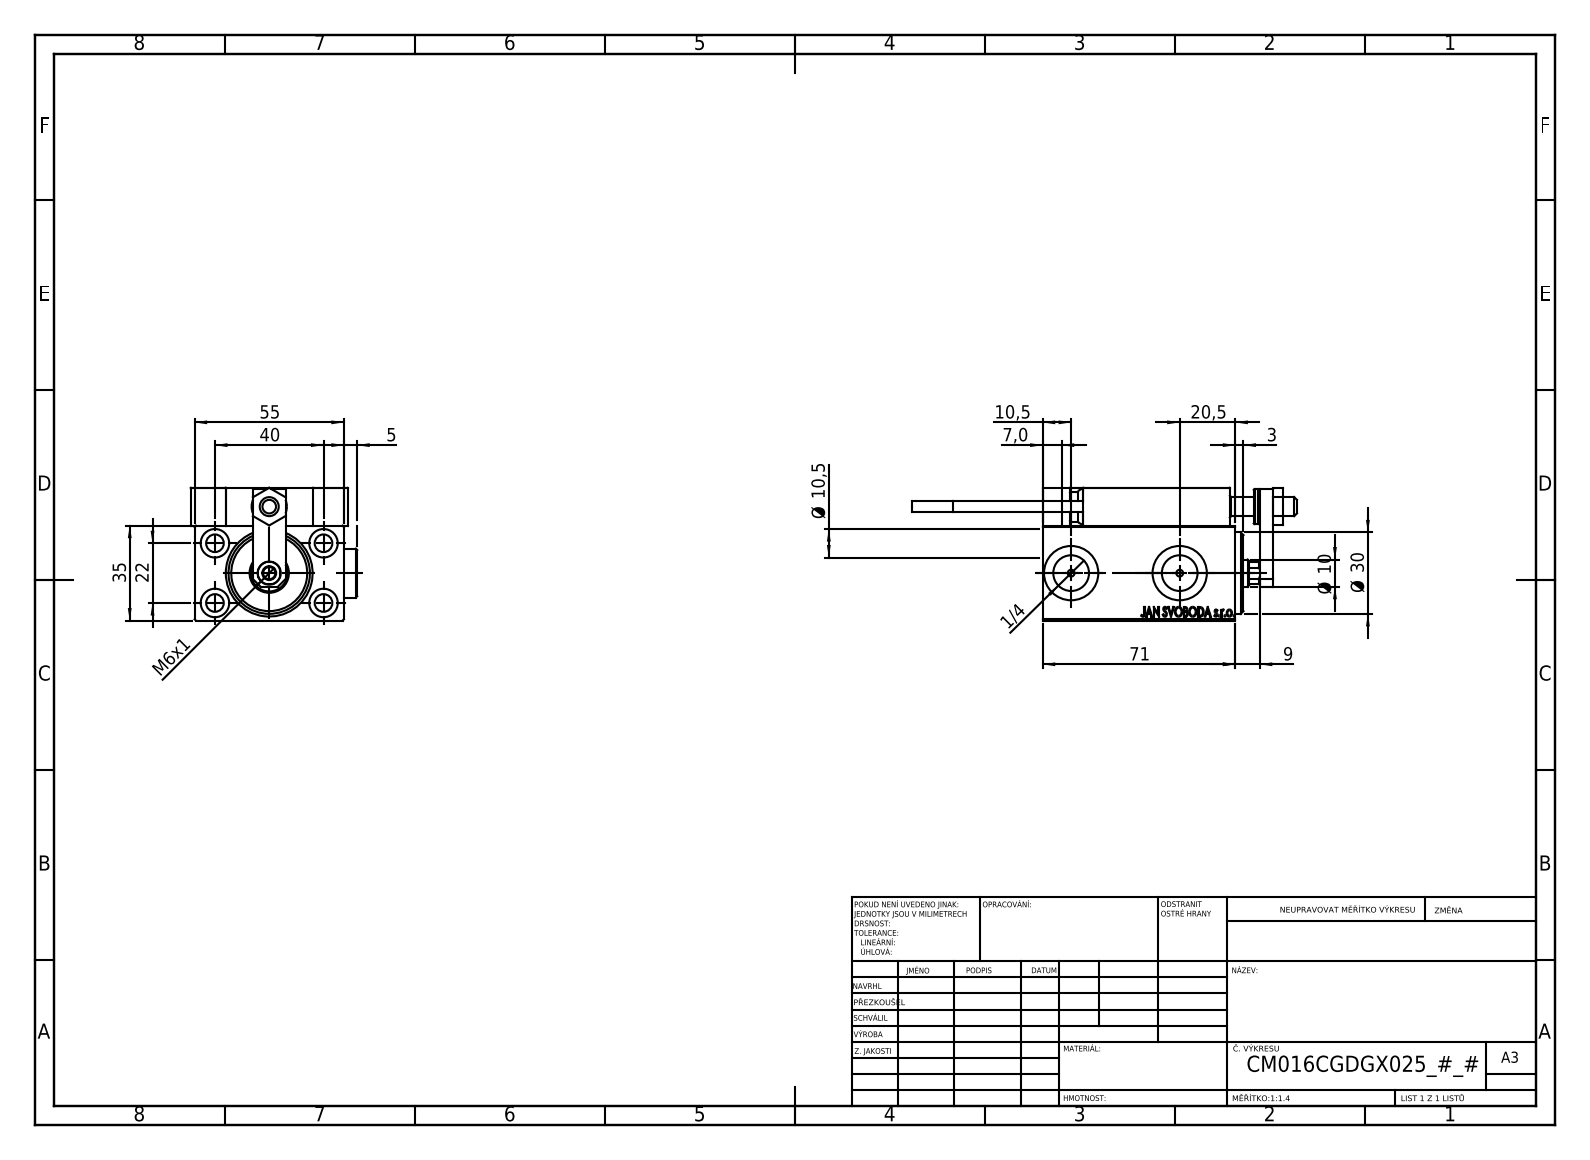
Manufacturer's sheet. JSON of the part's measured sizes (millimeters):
{"part_name": "NUT_D12; SWITCH X; SWITCH DIM B,W; MAGNET (+7 more)", "step_written_by": "SolidWorks 2019 (CONFIG_CONTROL_DESIGN)", "units": "millimeters", "bodies": {"solids": 25, "faces": 1339, "planar": 595, "cylindrical": 206, "other": 538}, "overall_size": [141.7, 61.4, 49], "volume_mm3": 160421, "surface_area_mm2": 58207, "round_holes": [[8, 5], [3.2, 4], [4, 4], [6.5, 4], [10.5, 4], [2.5, 2], [5, 2], [13.16, 2], [20, 2], [4.5, 1], [7, 1], [8.5, 1]], "round_bosses_or_shafts": [[18, 2], [5, 2], [3.8, 2], [13, 1], [11, 1]], "partial_cylinders_radius": [[0.3, 30], [3, 2], [4.5, 1]], "face_to_face_distances": [35, 5, 49, 14, 10, 3, 7, 55, 1.5, 59], "hole_center_spacings": [22.83, 40, 11.37, 20, 22, 23.09, 24.13, 29.59]}
